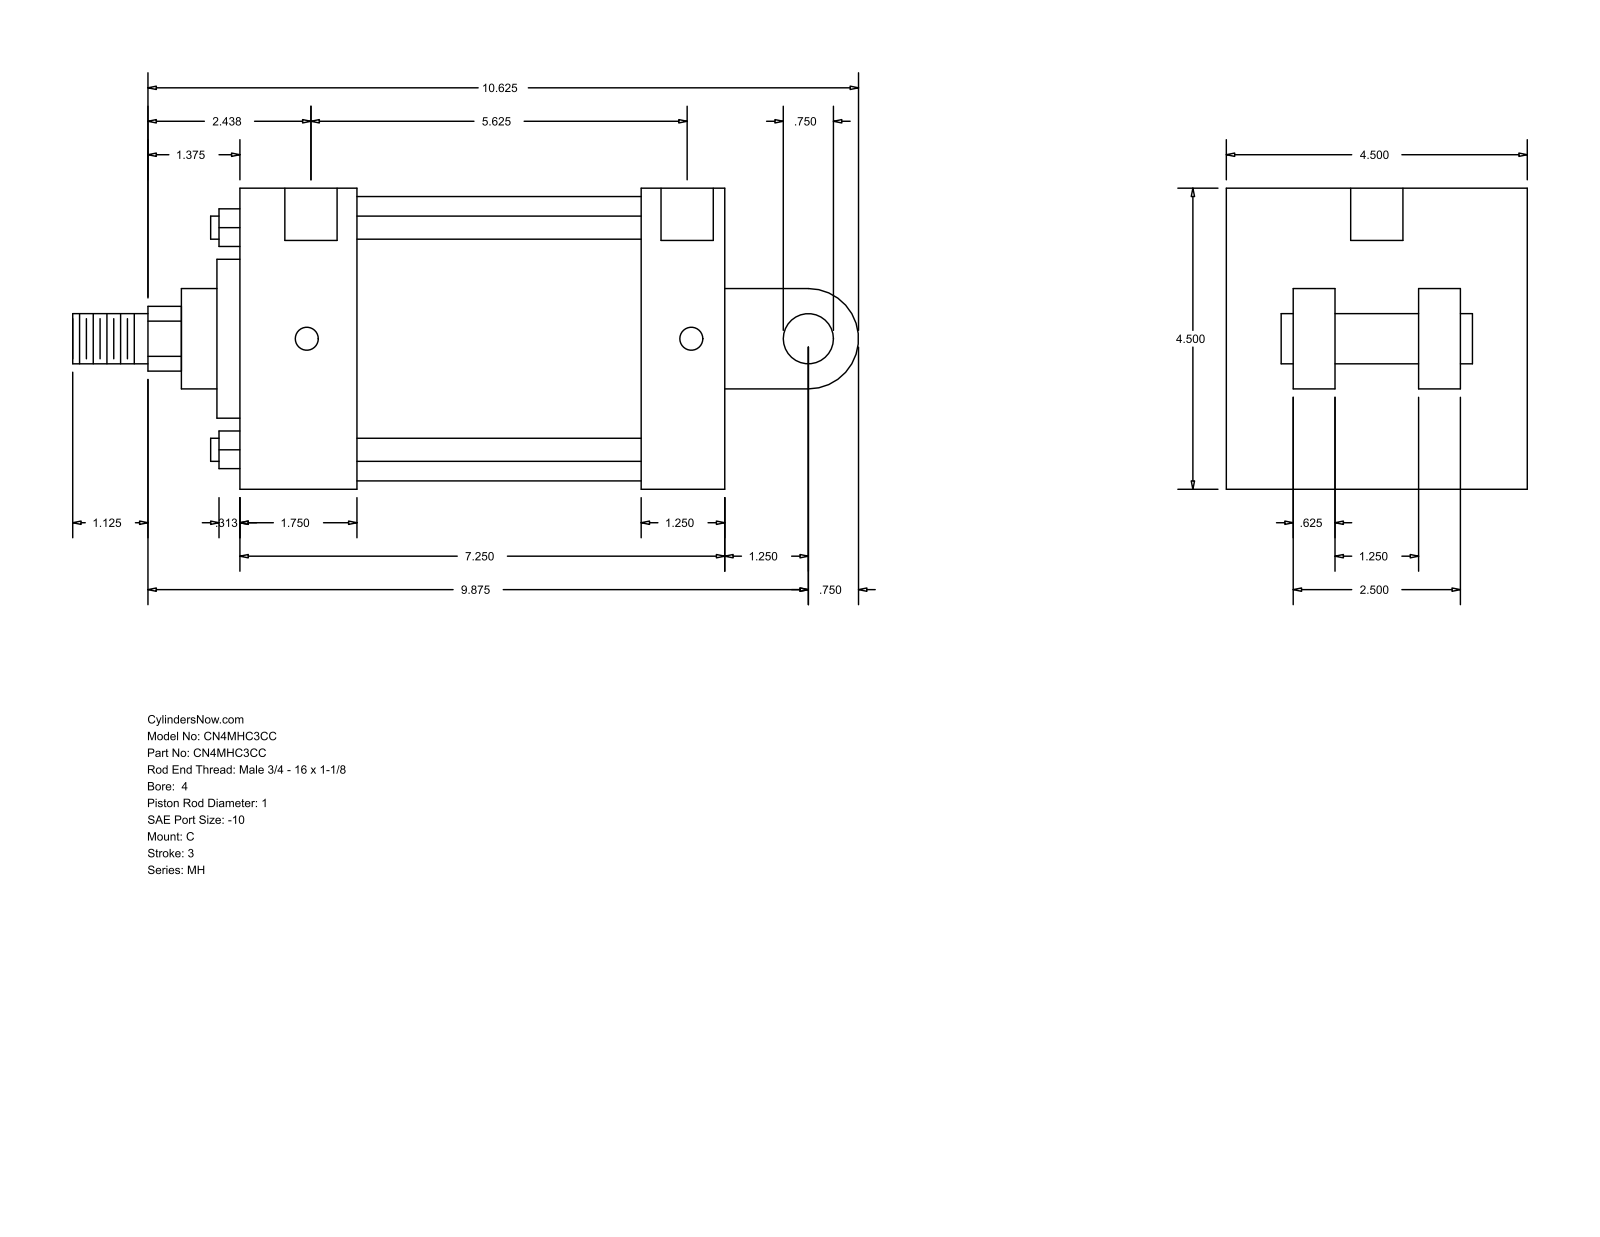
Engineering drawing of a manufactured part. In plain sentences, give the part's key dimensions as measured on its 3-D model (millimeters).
The part is named "MH_C__0400_1". Its 3-D file was written by "GSSL Pune (CONFIG_CONTROL_DESIGN)". It is 0 solids with 101 faces: 71 planar, 30 cylindrical and 0 other. Overall it measures 298.45 by 114.3 by 114.3 millimeters. Round holes: 4 of diameter 8.73, 2 of diameter 19.84. Round bosses or shafts: 4 of diameter 8.76, 2 of diameter 19.05, 1 of diameter 107.95, 1 of diameter 60.33, 1 of diameter 38.1, 1 of diameter 25.4. Partial cylindrical surfaces (rounded edges, fillets, slot ends): 1 of radius 12.29, 1 of radius 19.05. The main face-to-face distances are 114.3, 184.15, 44.46, 152.4, 107.94, 139.69, 31.75, 73.03, 41.27, 38.1. The hole center spacings are 146.05, 1.58, 1.59, 142.88, 144.46, 144.47.
